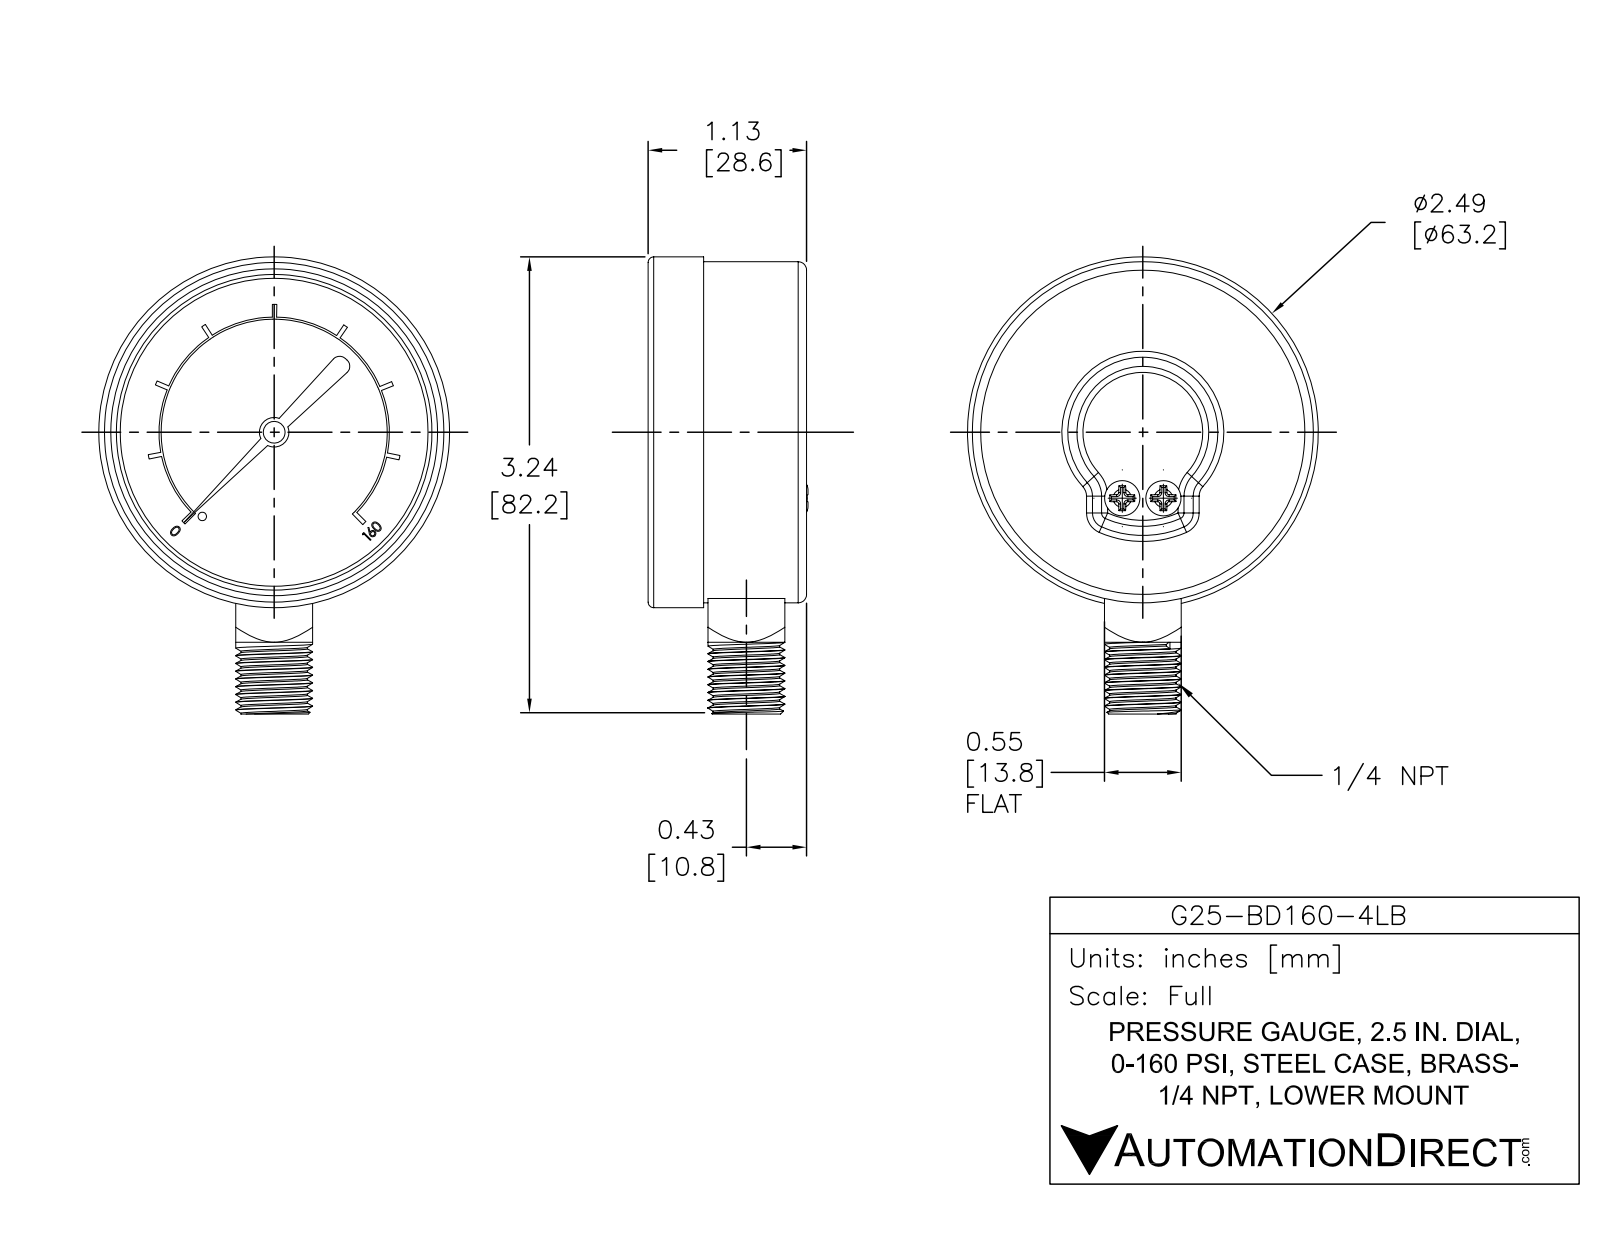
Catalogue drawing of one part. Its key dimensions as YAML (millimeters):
part_name: "G25-BD160-4LB"
step_written_by: "SolidWorks 2021 (AUTOMOTIVE_DESIGN)"
units: millimeters
bodies: {solids: 1, faces: 217, planar: 118, cylindrical: 35, other: 64}
overall_size: [82.4, 63.2, 28.8]
volume: 70270
surface_area: 14450
round_holes:
  - {diameter: 3.6, count: 1}
  - {diameter: 55.5, count: 1}
round_bosses_or_shafts:
  - {diameter: 6.4, count: 2}
  - {diameter: 63.2, count: 1}
  - {diameter: 61.5, count: 1}
  - {diameter: 13.8, count: 1}
  - {diameter: 3.9, count: 1}
  - {diameter: 3.1, count: 1}
  - {diameter: 1.5, count: 1}
partial_cylinders:
  - {radius: 1.5, count: 6}
  - {radius: 2.7, count: 1}
  - {radius: 20.4, count: 1}
  - {radius: 20.8, count: 1}
face_to_face_distances: [21.2, 2.5, 18.7, 28.6, 26, 7.4, 13.8, 18.6, 16, 2.6]
